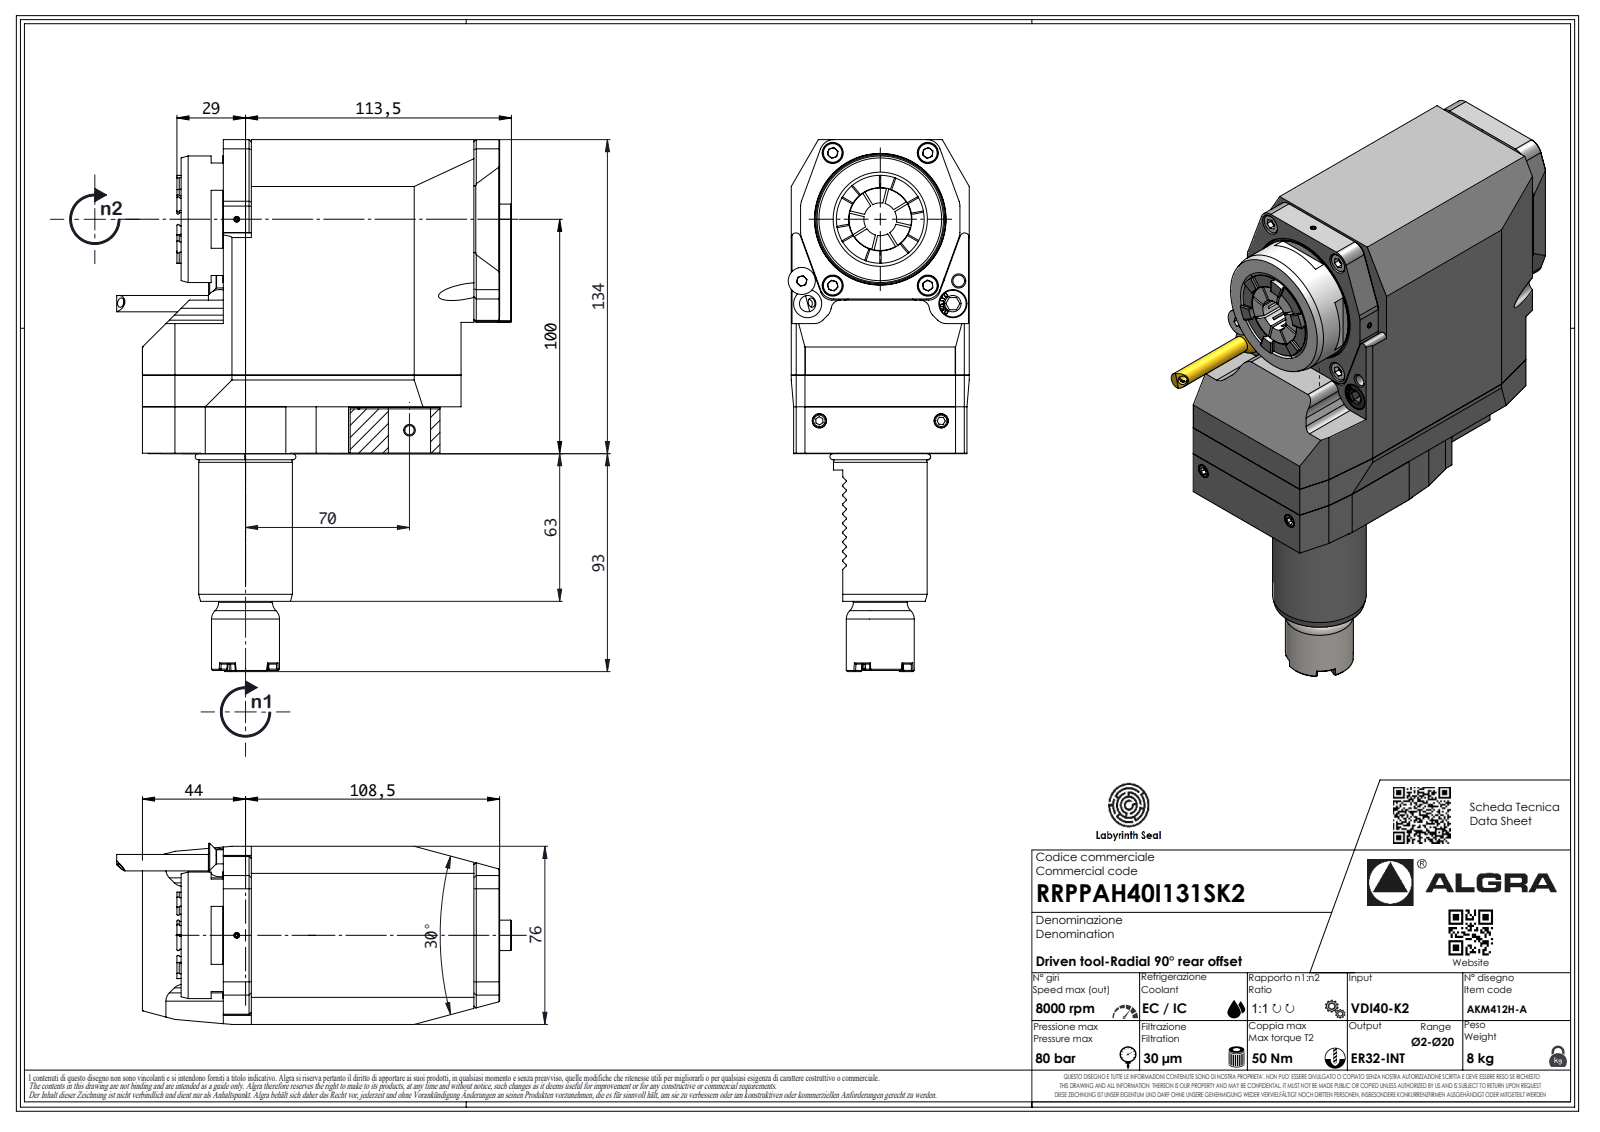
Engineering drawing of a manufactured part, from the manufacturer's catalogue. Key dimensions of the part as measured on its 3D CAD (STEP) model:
Part name (STEP PRODUCT): RRPPAH40I131SK2
STEP written by: SolidWorks 2023 (AUTOMOTIVE_DESIGN)
Units: millimetres
Bodies: 1 solid, 678 faces (434 planar, 87 cylindrical, 157 other)
Overall size (bounding box): 227 × 168.5 × 76
Volume: 1 299 000 mm³ · Surface area: 91 558 mm²
Round holes (diameter × count): ⌀2.1 ×1, ⌀20 ×1
Round bosses / shafts (diameter × count): ⌀54 ×1, ⌀40 ×1, ⌀38.7 ×1, ⌀29 ×1, ⌀23 ×1, ⌀7 ×1, ⌀6.37 ×1, ⌀1.7 ×1
Partial cylindrical surfaces — rounded edges, fillets, slot ends (radius × count): R0.3 ×10, R6 ×10, R0.33 ×7, R0.52 ×7, R3.7 ×7, R5 ×6, R0.5 ×2, R2 ×2
Main face-to-face distances: 76, 134, 16.5, 136, 20, 114, 18, 19.75, 152.5, 34.5
